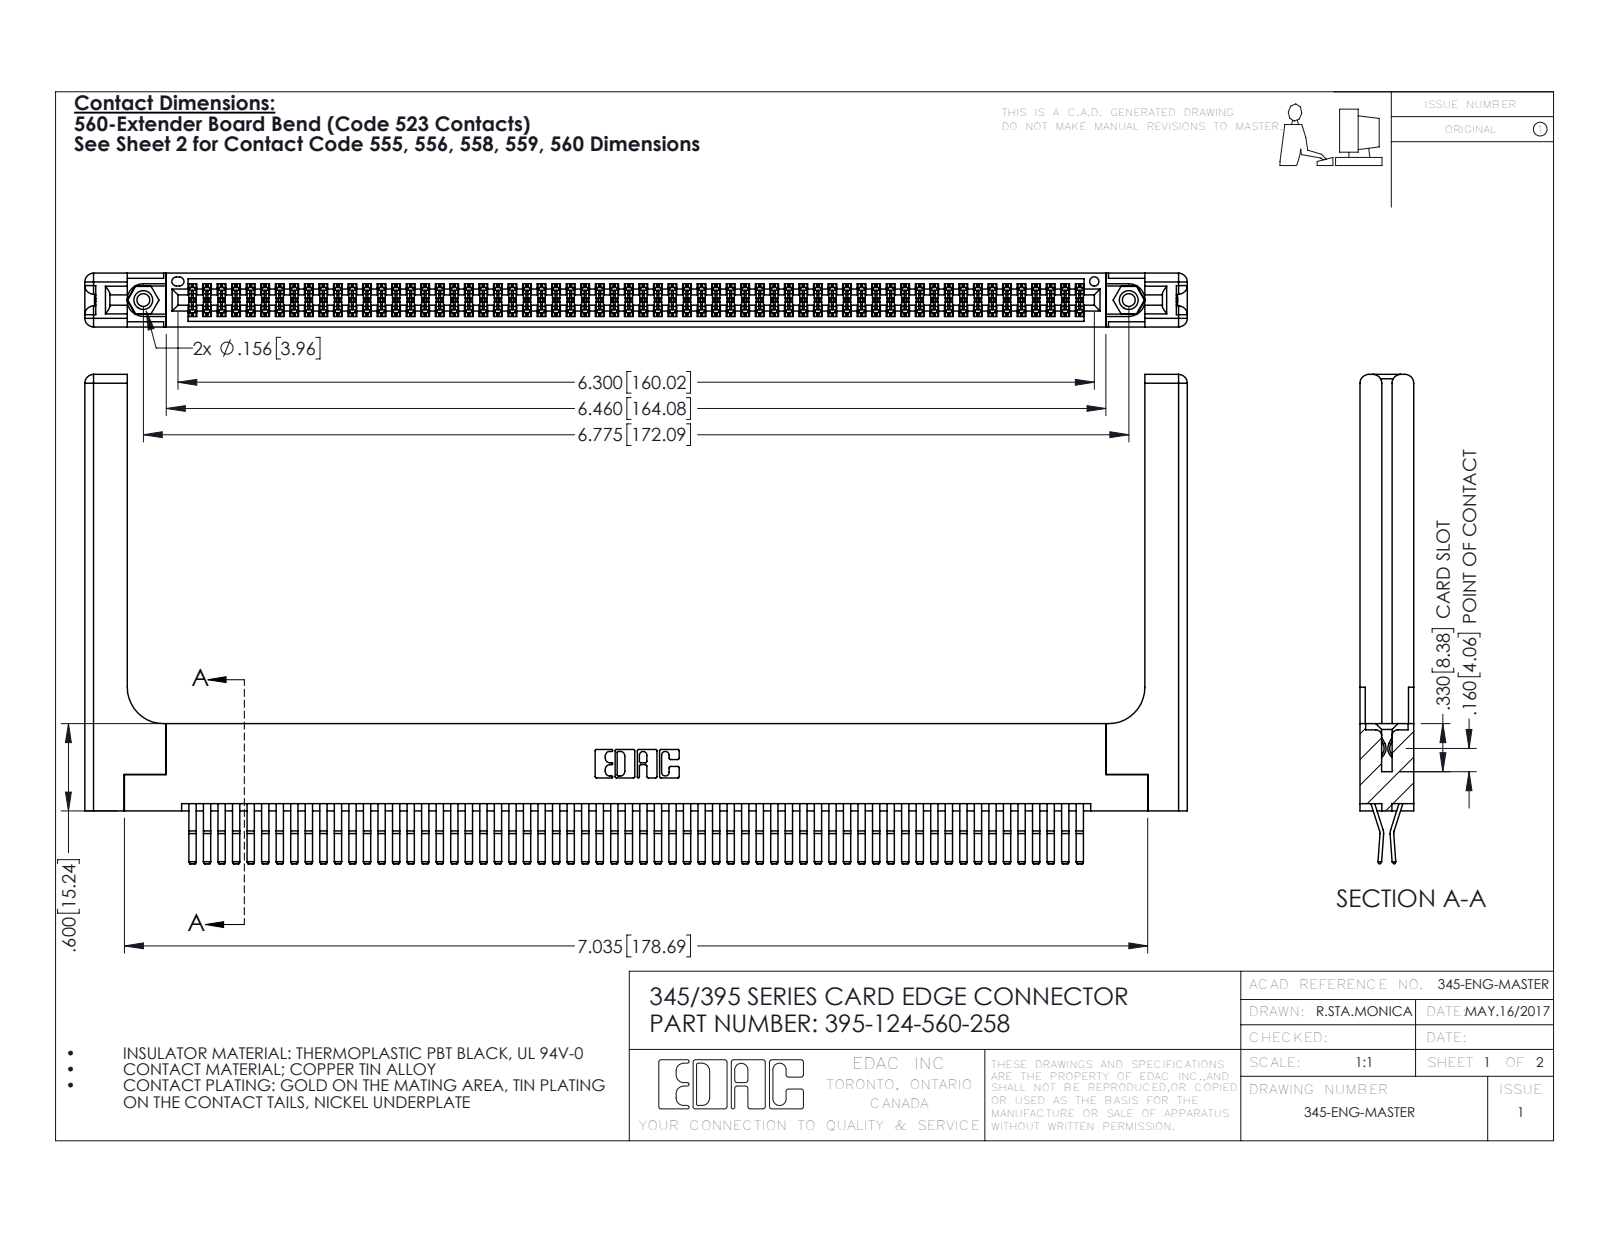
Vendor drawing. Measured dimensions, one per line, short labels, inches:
name: 345-292-001_560 Tail; 395-124-560-258; 345-220-058_345-220-058; 345-250-001_345-250-001-102 (+1 more)
written by: SolidWorks 2016 (CONFIG_CONTROL_DESIGN)
unit: in
bodies: 129 solids, 6830 faces (4320 planar, 2450 cylindrical, 60 other)
size: 7.579 × 3.362 × 0.37
volume: 1.719 in³; area: 56.81 in²
holes: 2× ⌀0.089, 2× ⌀0.125, 2× ⌀0.156, 1× ⌀0.064
bosses: 2× ⌀0.155
rounds: 187× R0.006, 22× R0.01, 16× R0.06, 6× R0.007, 6× R0.031, 3× R0.026, 2× R0.01, 2× R0.014
face distances: 0.072, 0.298, 0.025, 0.37, 0.2, 0.098, 0.272, 0.225, 0.15, 0.148
hole spacings: 0.27, 6.539, 6.775
